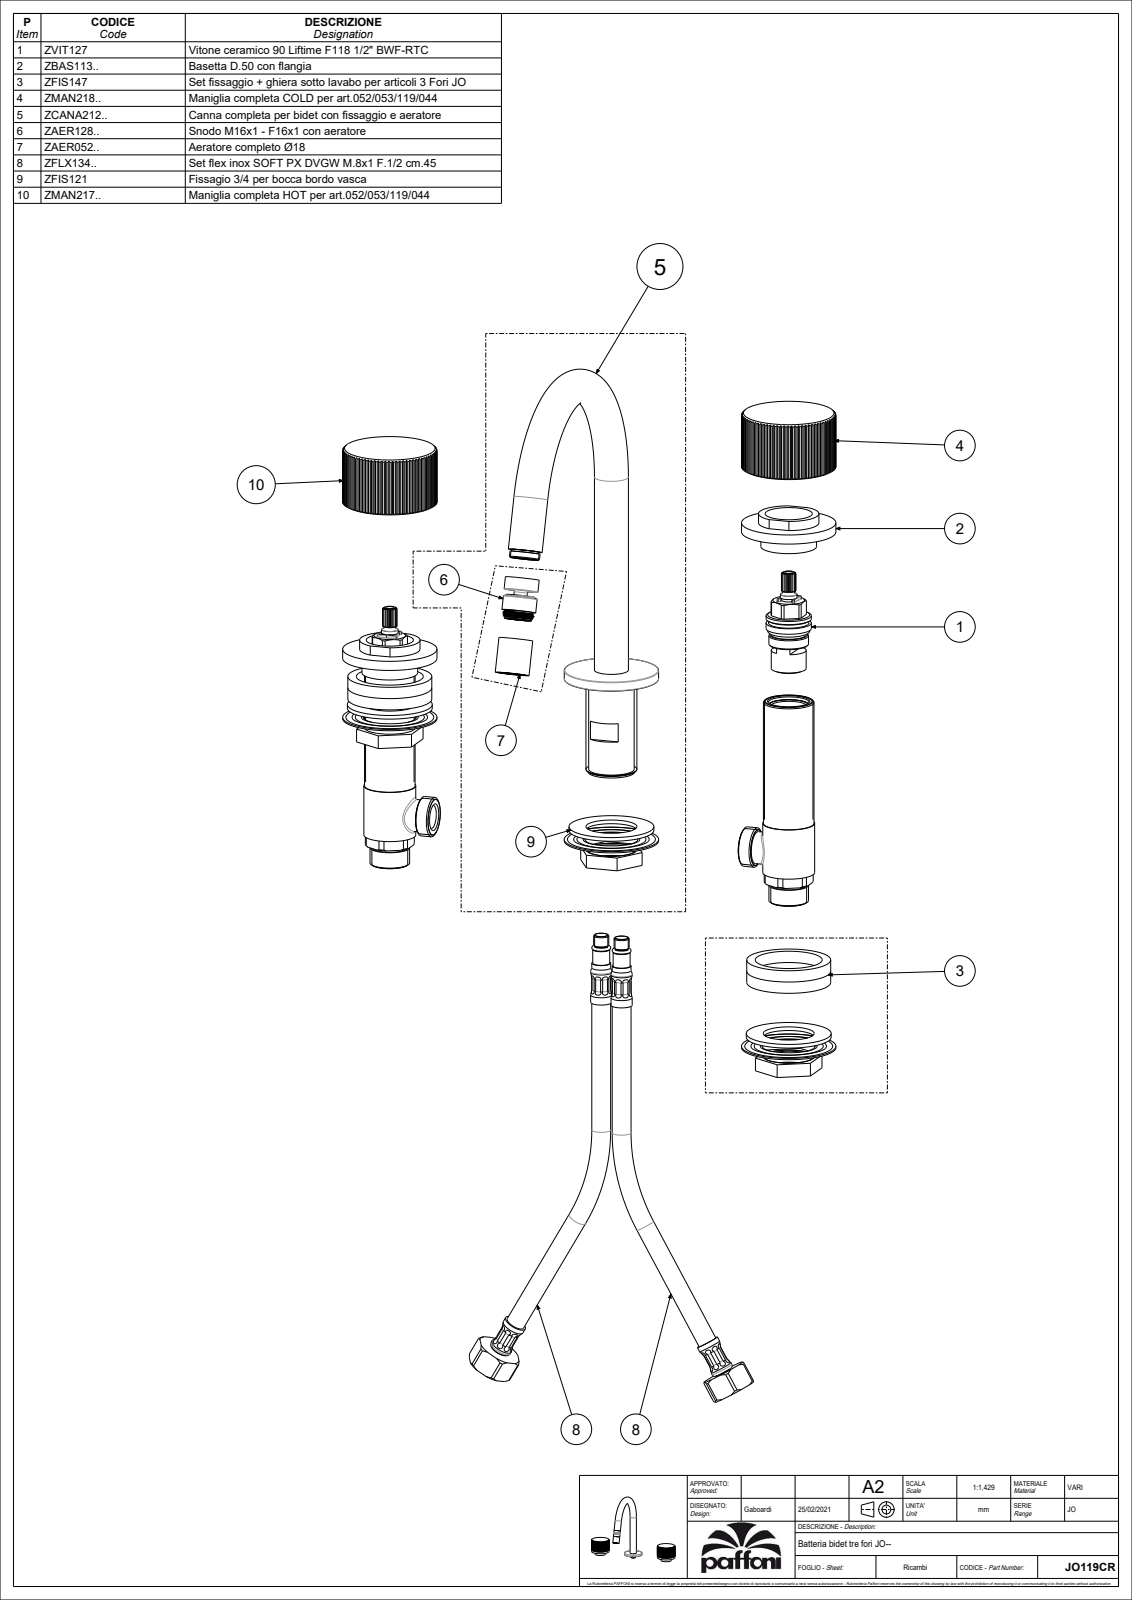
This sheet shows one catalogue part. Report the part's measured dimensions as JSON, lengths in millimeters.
{"part_name": "JO119CR", "step_written_by": "CREO PARAMETRIC BY PTC INC, 2020044 (CONFIG_CONTROL_DESIGN)", "units": "millimeters", "bodies": {"solids": 8, "faces": 920, "planar": 510, "cylindrical": 314, "other": 96}, "overall_size": [290, 184, 179.44], "volume_mm3": 108811, "surface_area_mm2": 89738, "round_holes": [[15, 3], [3, 2], [3.3, 2], [4.2, 2], [4.25, 2], [5.5, 2], [8, 2], [16, 2], [25, 2], [41, 2], [46.2, 2], [47, 2]], "round_bosses_or_shafts": [[50, 3], [18, 3], [44, 2], [41.2, 2], [24, 2], [22, 2], [21.4, 2], [15.9, 2]], "partial_cylinders_radius": [[0.2, 52], [1, 4], [9.4, 2], [16, 2]], "face_to_face_distances": [5, 33.7, 28.7, 34.66, 34.64, 2.5, 0.5, 3.7, 2, 10], "hole_center_spacings": [120, 240]}
